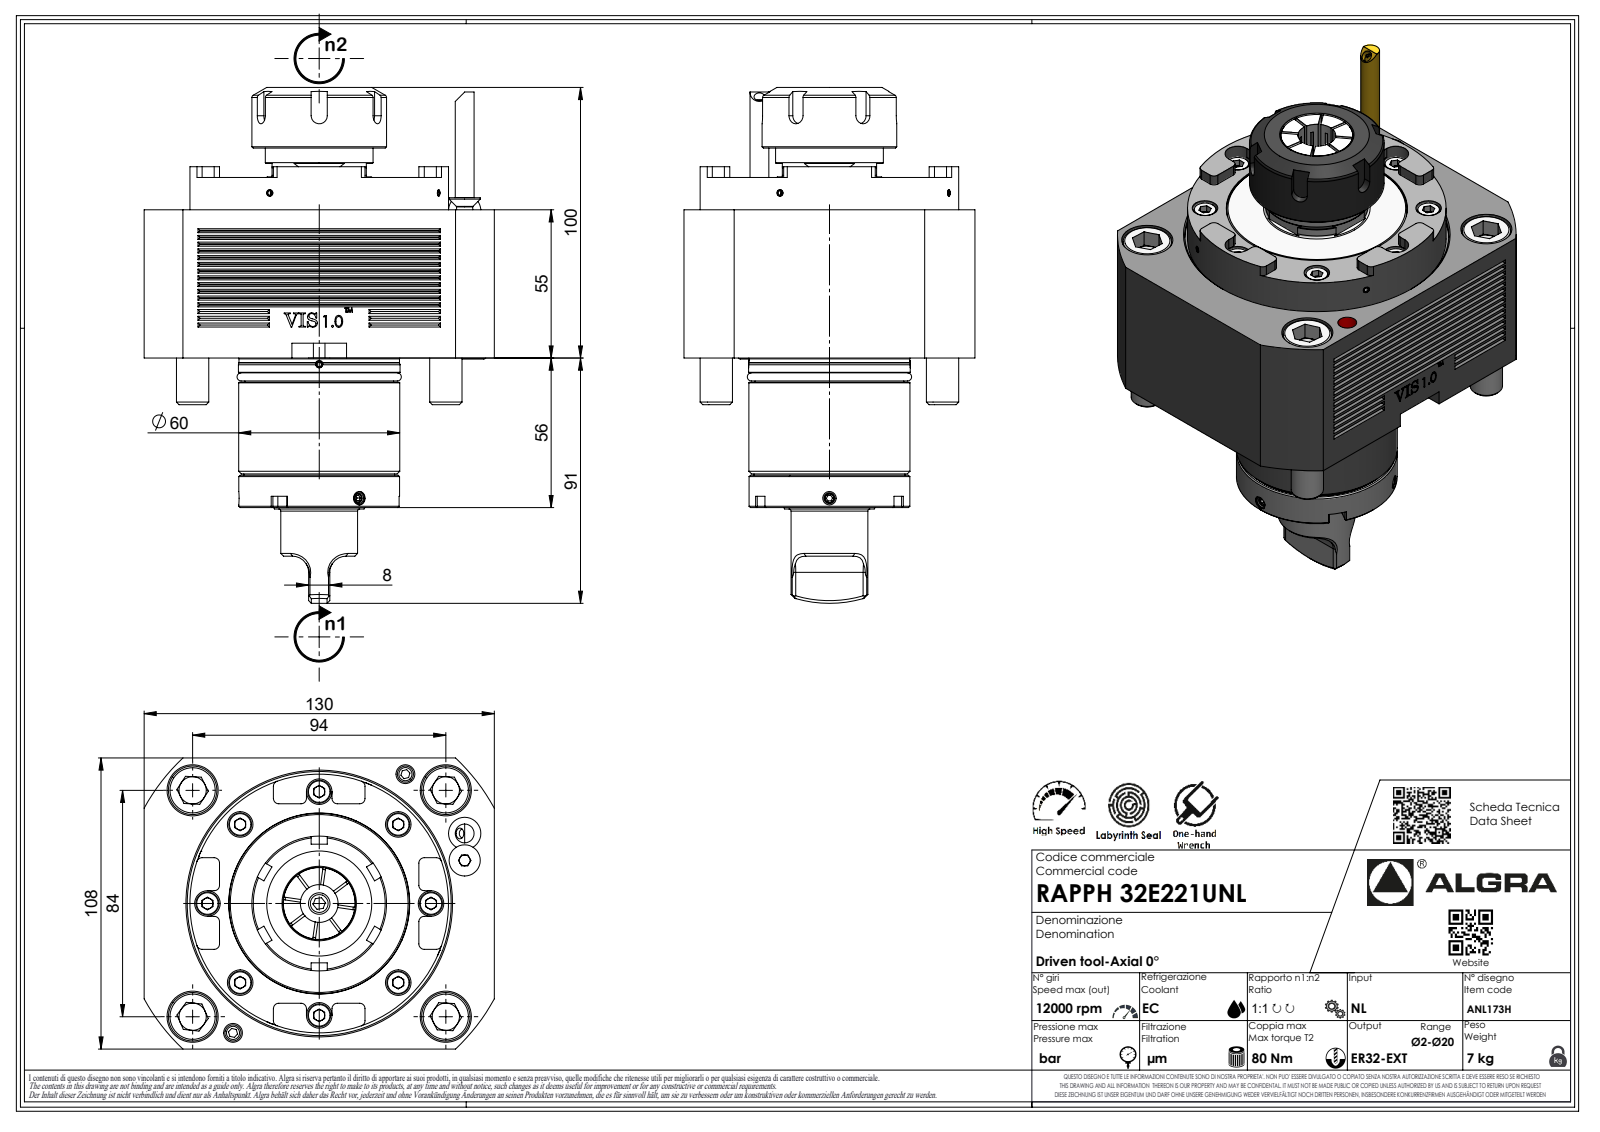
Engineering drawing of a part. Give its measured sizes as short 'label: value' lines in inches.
name: RAPPH32E221UNL
written by: SolidWorks 2023 (AUTOMOTIVE_DESIGN)
unit: in
bodies: 1 solid, 485 faces (299 planar, 85 cylindrical, 101 other)
size: 7.536 × 5.118 × 4.252
volume: 64.99 in³; area: 119.3 in²
holes: 1× ⌀0.083, 1× ⌀0.157
bosses: 1× ⌀3.78, 1× ⌀2.362, 1× ⌀2.354, 1× ⌀1.969, 1× ⌀1.575, 1× ⌀1.122, 1× ⌀0.276, 1× ⌀0.251
rounds: 25× R0.079, 7× R0.013, 7× R0.02, 7× R0.146, 6× R0.236, 4× R0.187, 3× R0.118, 1× R0.008
face distances: 2.165, 4.252, 2.638, 0.472, 5.118, 2.185, 4.35, 4.823, 6.138, 3.953
